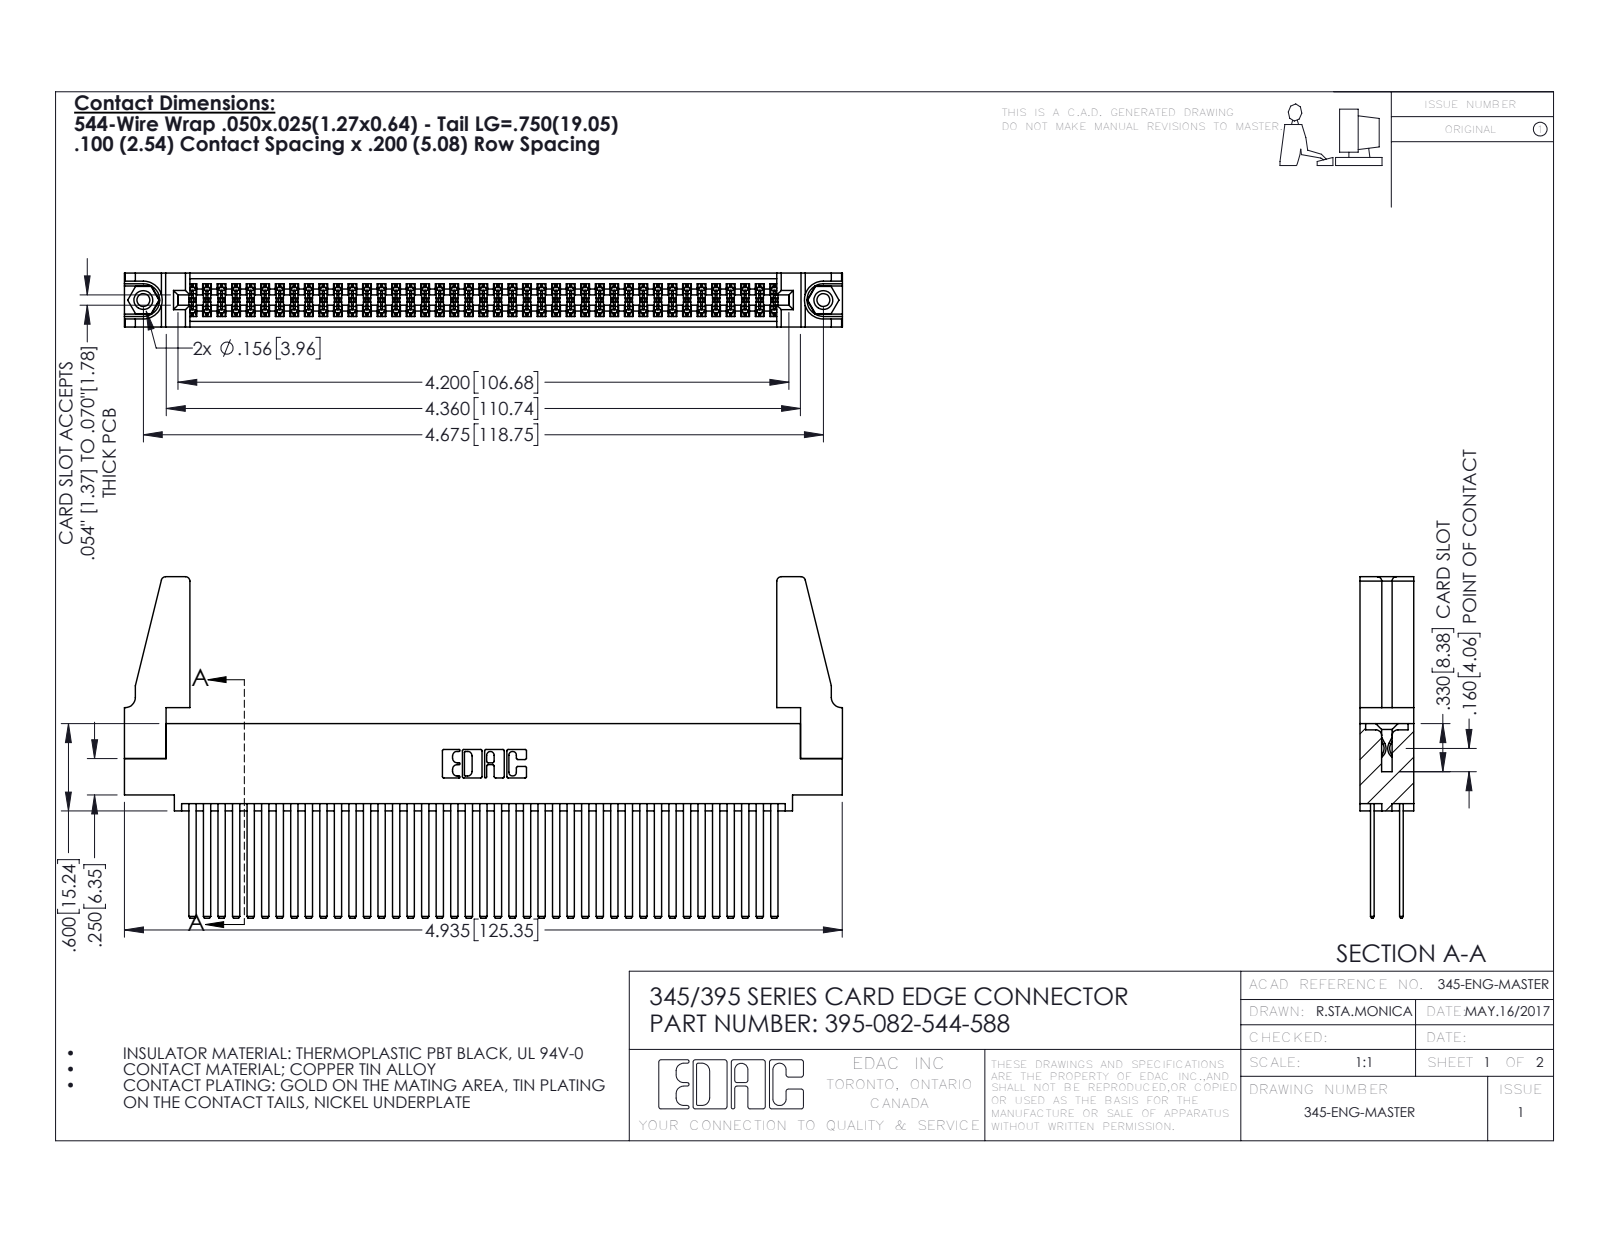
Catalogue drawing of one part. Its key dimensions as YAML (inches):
part_name: "345 Part_0.110 Offset - 0.156 Dia-TH; 395-082-544-588; 345-250-001_345-250-001-102; 345-220-078_345-220-088 (+1 more)"
step_written_by: "SolidWorks 2016 (CONFIG_CONTROL_DESIGN)"
units: inches
bodies: {solids: 87, faces: 3862, planar: 2534, cylindrical: 1312, other: 16}
overall_size: [4.936, 2.347, 0.37]
volume: 1.007
surface_area: 40.52
round_holes:
  - {diameter: 0.089, count: 2}
  - {diameter: 0.125, count: 2}
  - {diameter: 0.156, count: 2}
  - {diameter: 0.064, count: 1}
round_bosses_or_shafts:
  - {diameter: 0.155, count: 2}
partial_cylinders:
  - {radius: 0.006, count: 123}
  - {radius: 0.01, count: 22}
  - {radius: 0.03, count: 8}
  - {radius: 0.007, count: 6}
  - {radius: 0.031, count: 6}
  - {radius: 0.026, count: 3}
  - {radius: 0.014, count: 2}
  - {radius: 0.019, count: 2}
face_to_face_distances: [0.072, 0.298, 0.2, 0.098, 0.272, 0.025, 0.225, 0.37, 0.175, 0.149]
hole_center_spacings: [0.27, 4.439, 4.675]
